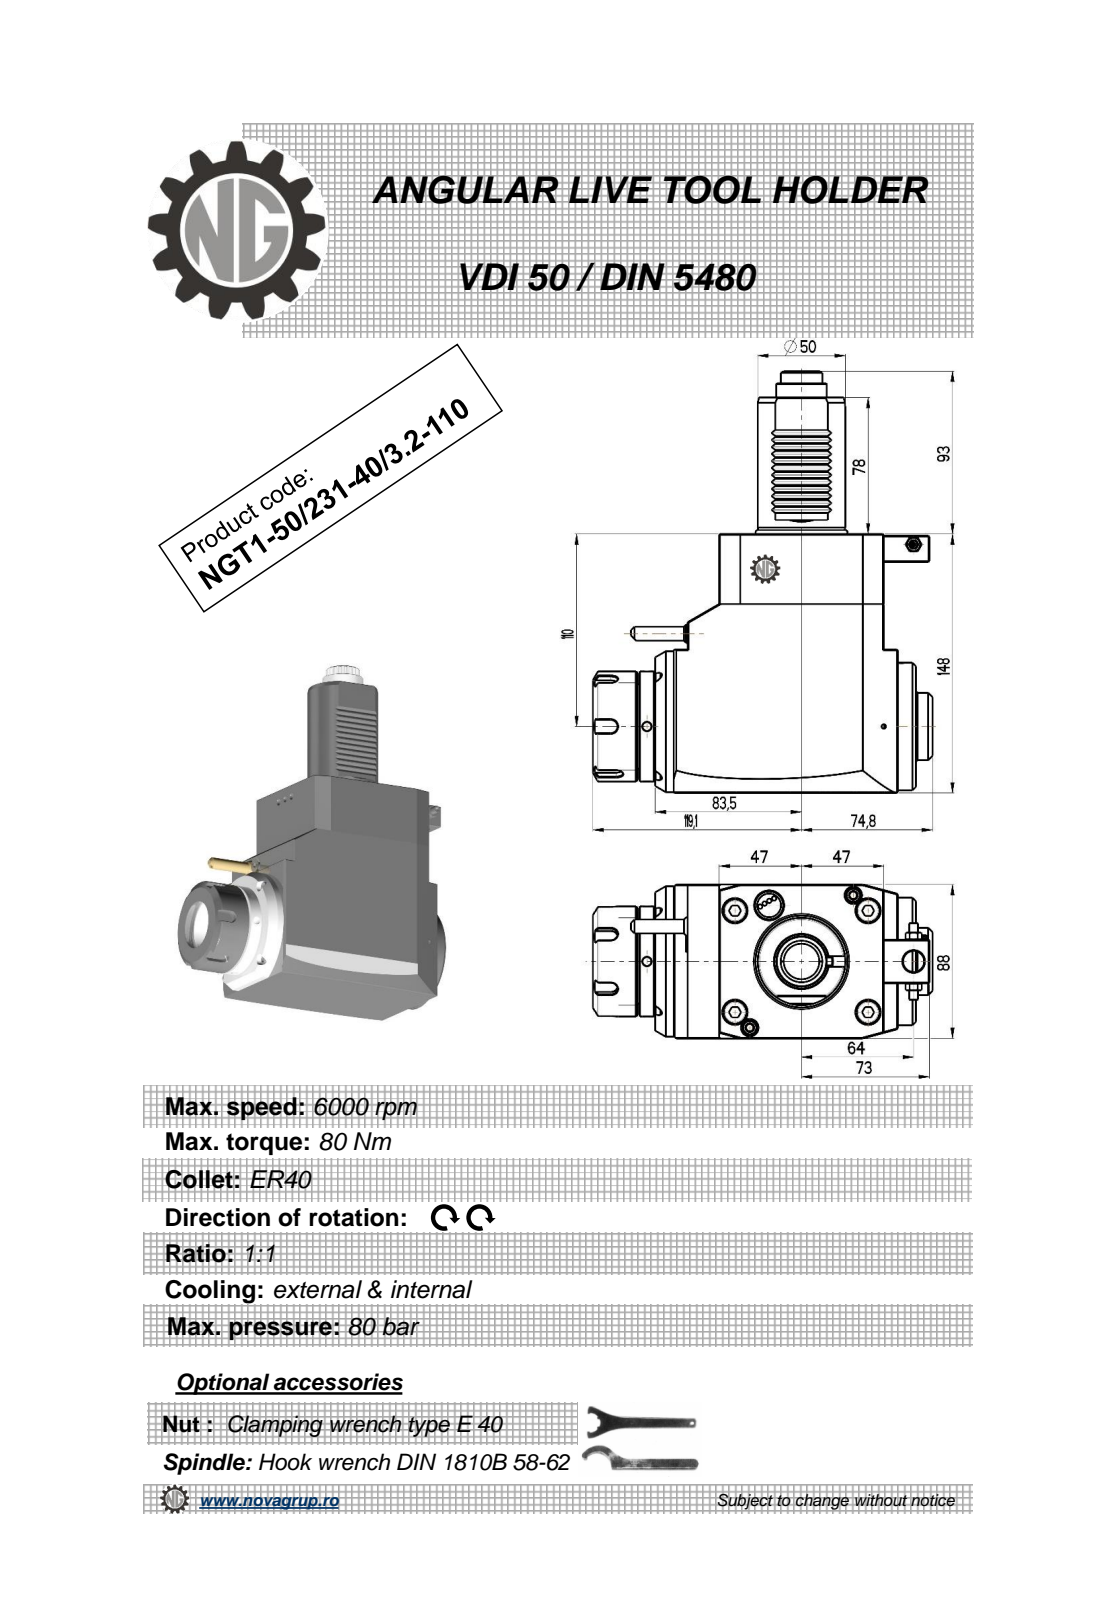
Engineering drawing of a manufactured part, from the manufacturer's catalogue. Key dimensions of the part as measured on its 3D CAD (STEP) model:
Part name (STEP PRODUCT): NGT1_50_231_40_3_2_110
STEP written by: PRO/ENGINEER BY PARAMETRIC TECHNOLOGY CORPORATION, 2010280 (CONFIG_CONTROL_DESIGN)
Units: millimetres
Bodies: 1 solid, 525 faces (207 planar, 165 cylindrical, 153 other)
Overall size (bounding box): 241 × 193.9 × 88
Volume: 1 857 000 mm³ · Surface area: 115 788 mm²
Round holes (diameter × count): ⌀5 ×3, ⌀3 ×1, ⌀4.2 ×1, ⌀9.5 ×1, ⌀12 ×1, ⌀33.5 ×1
Round bosses / shafts (diameter × count): ⌀86 ×1, ⌀73 ×1, ⌀63 ×1, ⌀51 ×1, ⌀50 ×1, ⌀40 ×1, ⌀38.5 ×1, ⌀28.8 ×1
Partial cylindrical surfaces — rounded edges, fillets, slot ends (radius × count): R3.04 ×36, R0.26 ×12, R0.3 ×12, R0.2 ×6, R3.75 ×5, R10.56 ×1, R11.88 ×1, R17.5 ×1
Main face-to-face distances: 88, 148, 94, 8, 120, 36.5, 130.5, 148.8, 112.3, 18.3
Hole centre spacings: 52.46, 56.65, 101.5, 152.25, 184.38
